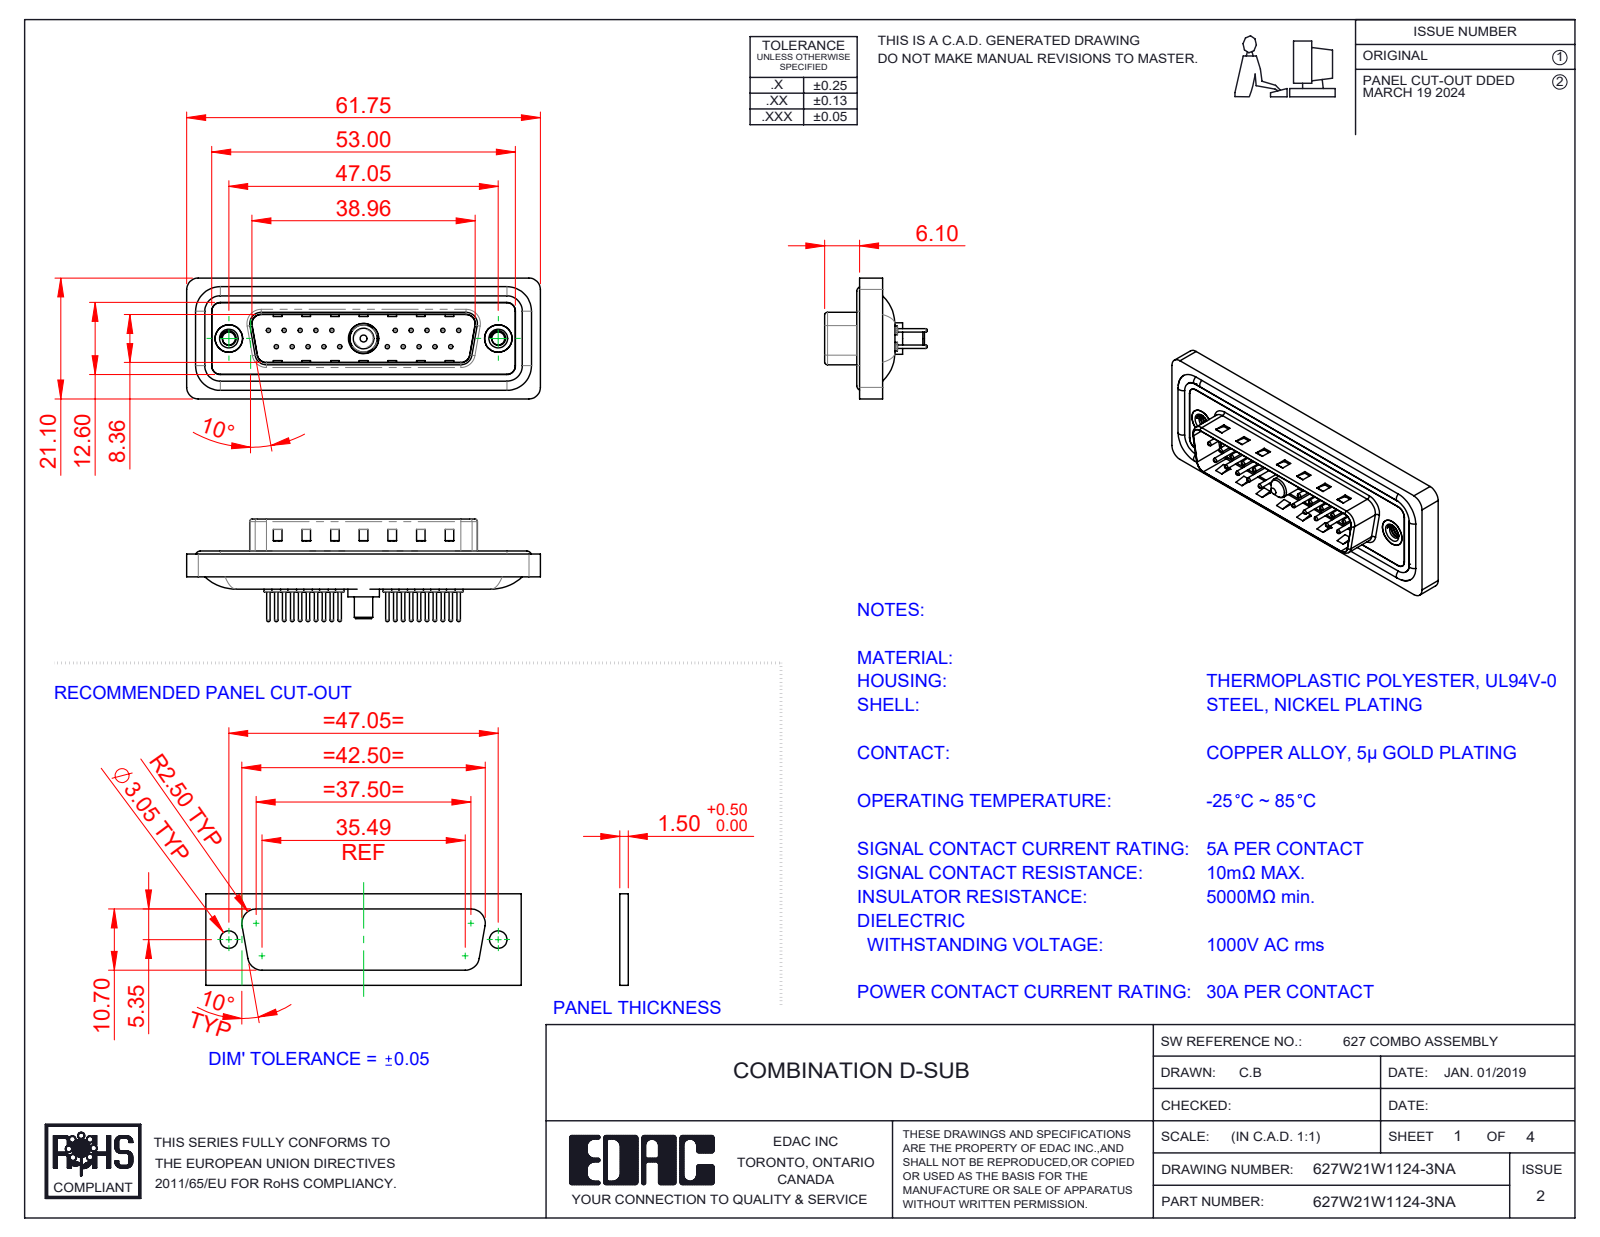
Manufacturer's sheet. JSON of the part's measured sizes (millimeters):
{"part_name": "627Combo Contact Row 2_24; 627Combo Threaded Rivet_A; Power Pin_30A S; 627Combo Shell Rear_25 Contacts (+5 more)", "step_written_by": "SolidWorks 2023 (CONFIG_CONTROL_DESIGN)", "units": "millimeters", "bodies": {"solids": 29, "faces": 1260, "planar": 359, "cylindrical": 489, "other": 412}, "overall_size": [61.75, 21.1, 17.9], "volume_mm3": 7206, "surface_area_mm2": 11955, "round_holes": [[0.75, 20], [1.6, 20], [2, 20], [2.26, 2], [4, 2], [4.8, 2], [5, 2], [4.85, 1], [5.3, 1]], "round_bosses_or_shafts": [[1.5, 20], [0.6, 20], [1.6, 4], [4.9, 2], [5.5, 1], [5.2, 1], [4.75, 1], [3.75, 1]], "partial_cylinders_radius": [[1.5, 22], [2, 18], [0.5, 8], [1.6, 8], [0.25, 4], [0.6, 4], [0.65, 4], [0.9, 4]], "face_to_face_distances": [0.4, 1.5, 1.1, 1.6, 0.5, 3.1, 2.9, 4.1, 0.82, 9.58], "hole_center_spacings": [3.16, 2.77, 5.54, 8.31, 5.04, 19.39, 20.97, 22.16]}
